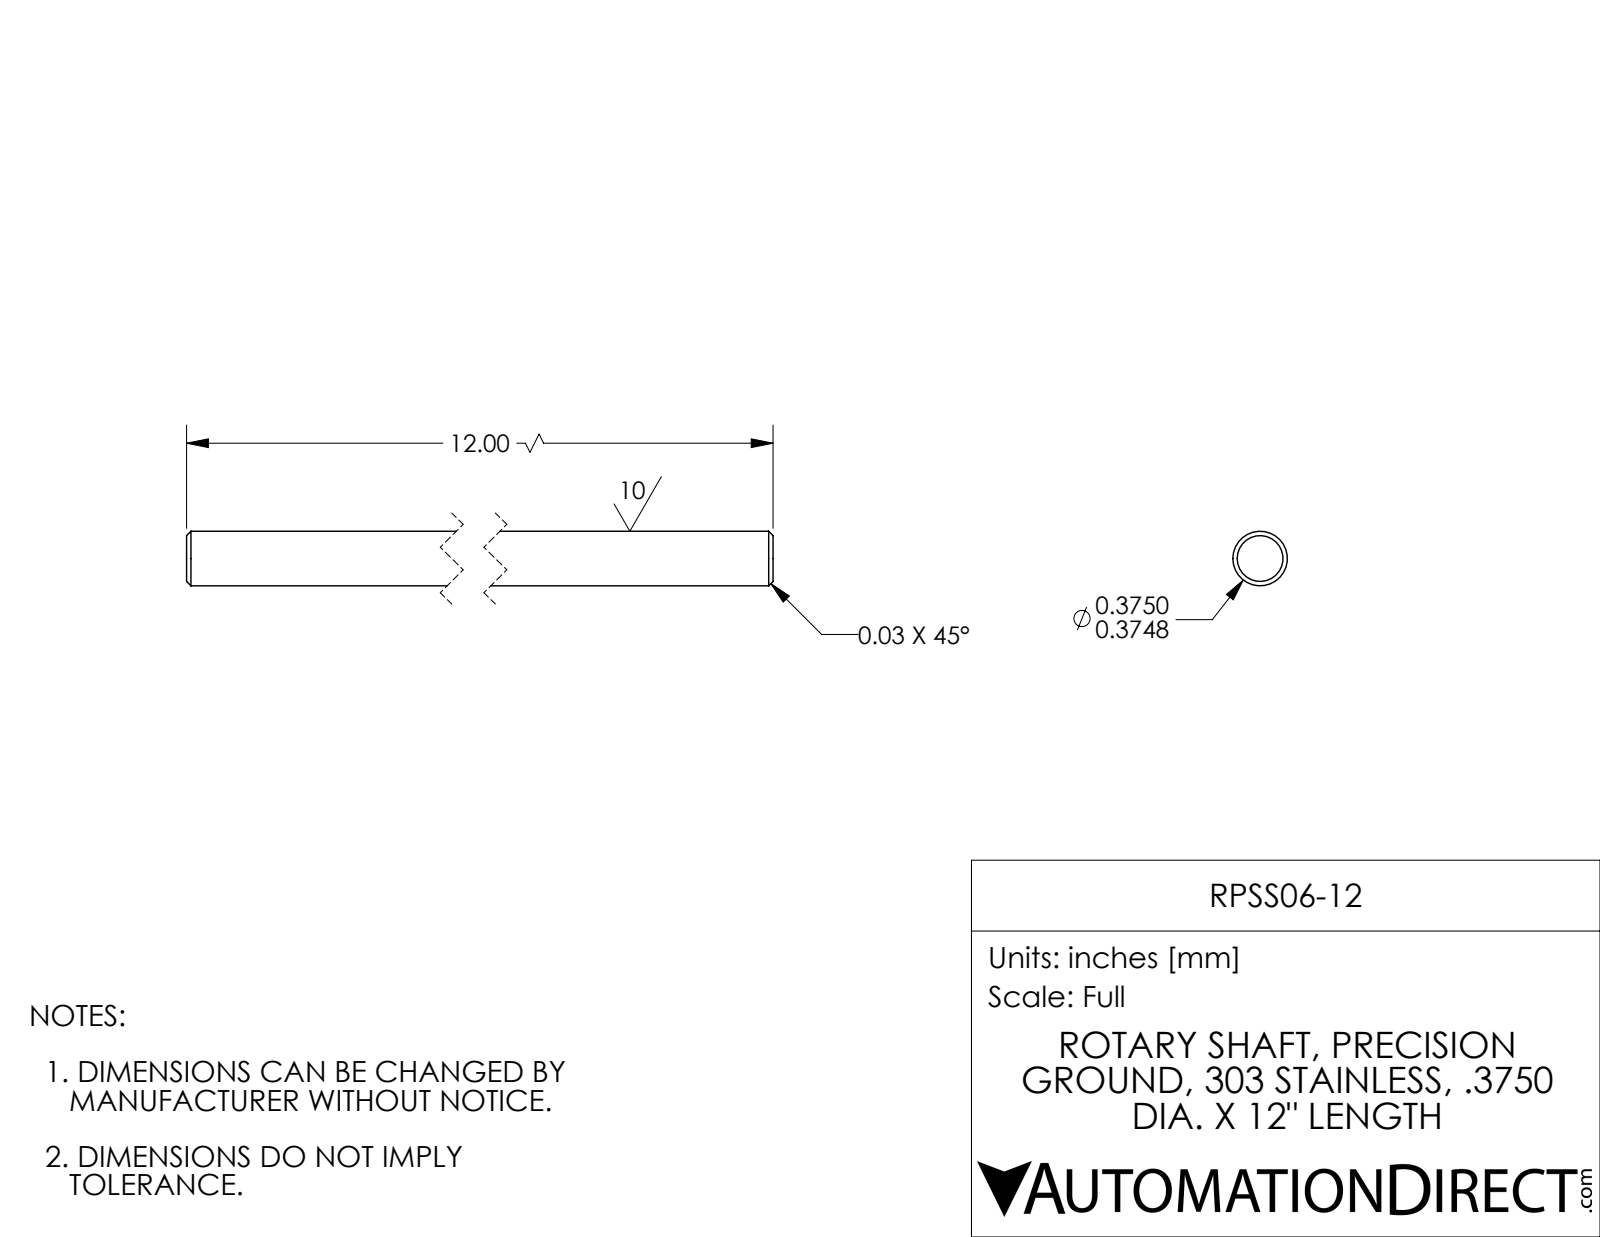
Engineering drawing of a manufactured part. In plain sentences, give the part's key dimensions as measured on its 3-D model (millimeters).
The part is named "RPSS06-12". Its 3-D file was written by "SolidWorks 2017 (AUTOMOTIVE_DESIGN)". It is 1 solid with 8 faces: 2 planar, 2 cylindrical and 4 other. Overall it measures 304.8 by 9.5 by 9.5 millimeters. Its volume is 21 700 cubic millimeters and its surface area 9 232 square millimeters. Round bosses or shafts: 1 of diameter 9.5. The main face-to-face distances are 304.8.
